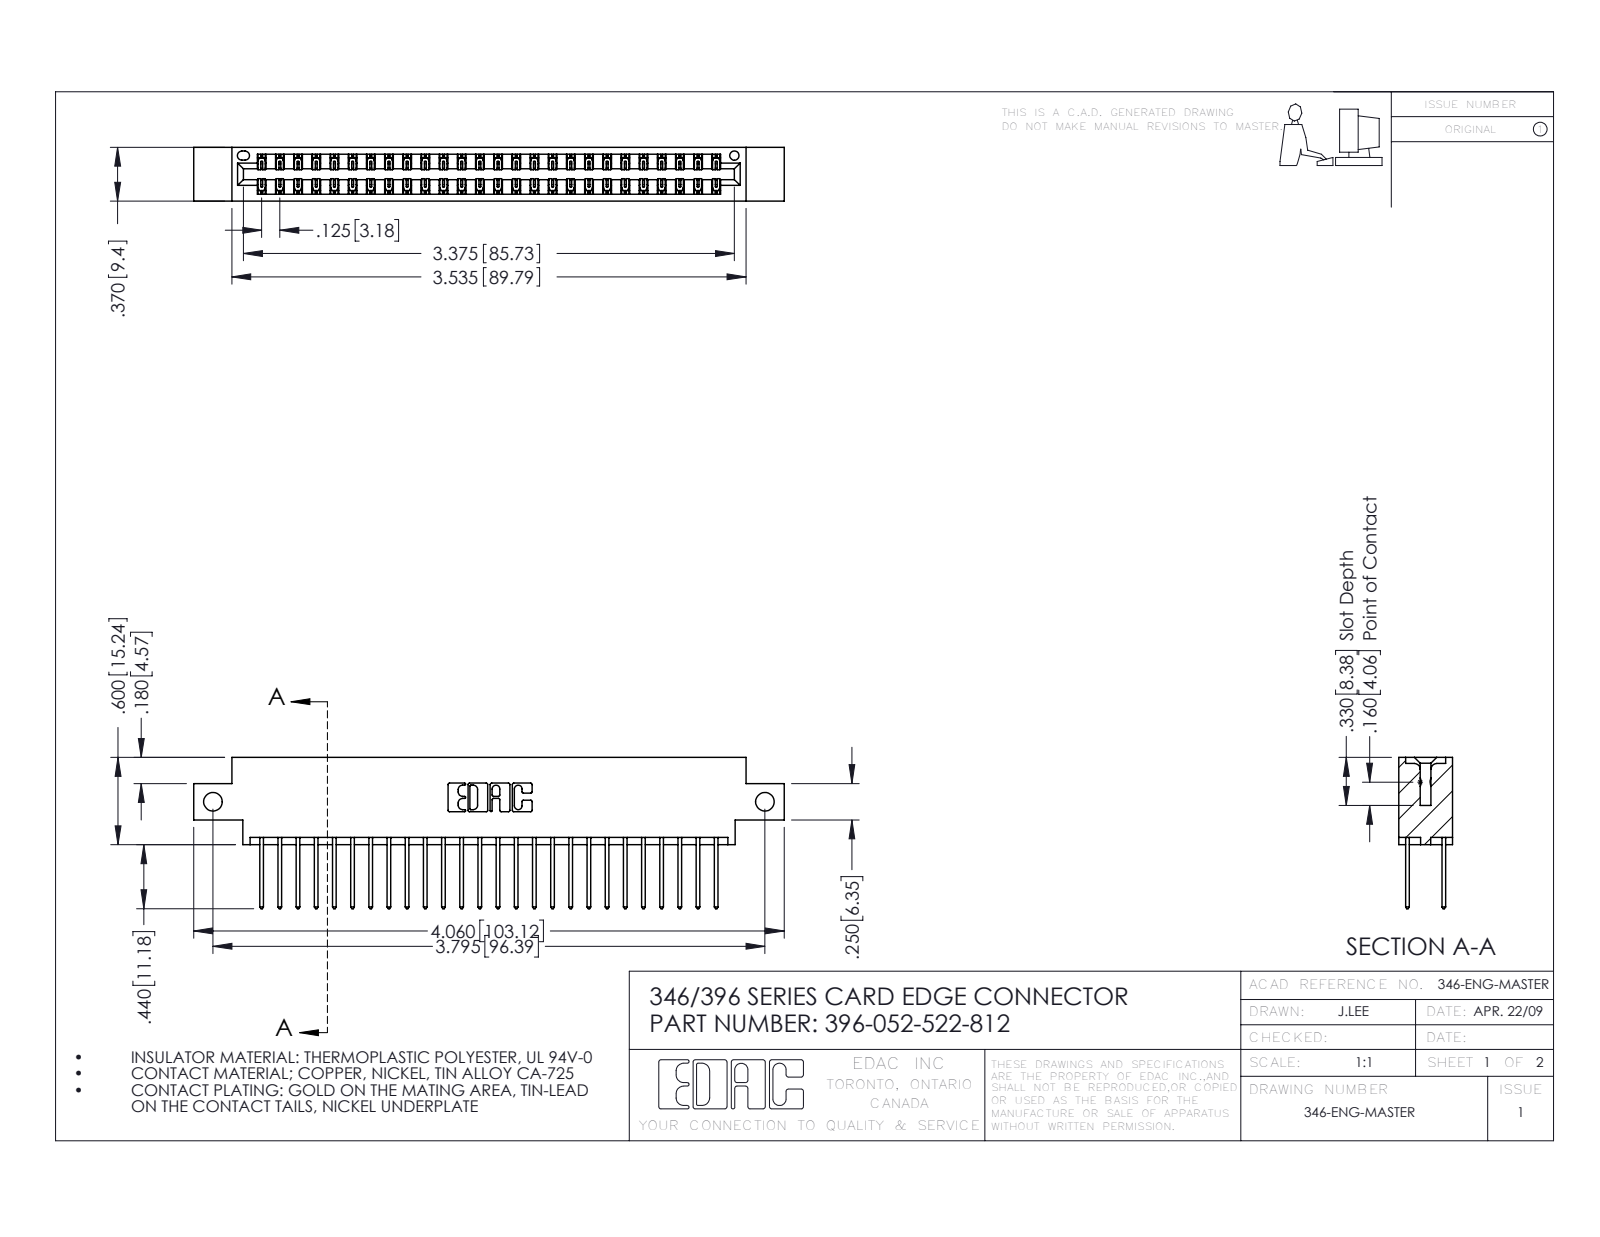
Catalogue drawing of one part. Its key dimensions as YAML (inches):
part_name: "396-052-522-812; 346 Part_0.170 Offset - Side Mount; 345-292-001_345-293-122"
step_written_by: "SolidWorks 2016 (CONFIG_CONTROL_DESIGN)"
units: inches
bodies: {solids: 53, faces: 2830, planar: 1900, cylindrical: 930, other: 0}
overall_size: [4.06, 1.04, 0.37]
volume: 0.599
surface_area: 21.56
round_holes:
  - {diameter: 0.128, count: 2}
  - {diameter: 0.064, count: 1}
partial_cylinders:
  - {radius: 0.006, count: 78}
  - {radius: 0.01, count: 52}
  - {radius: 0.01, count: 22}
  - {radius: 0.007, count: 6}
  - {radius: 0.031, count: 6}
  - {radius: 0.026, count: 3}
  - {radius: 0.014, count: 2}
  - {radius: 0.022, count: 2}
face_to_face_distances: [0.048, 0.322, 0.25, 0.37, 0.072, 0.298, 0.025, 0.275, 0.148, 0.222]
hole_center_spacings: [3.795]
